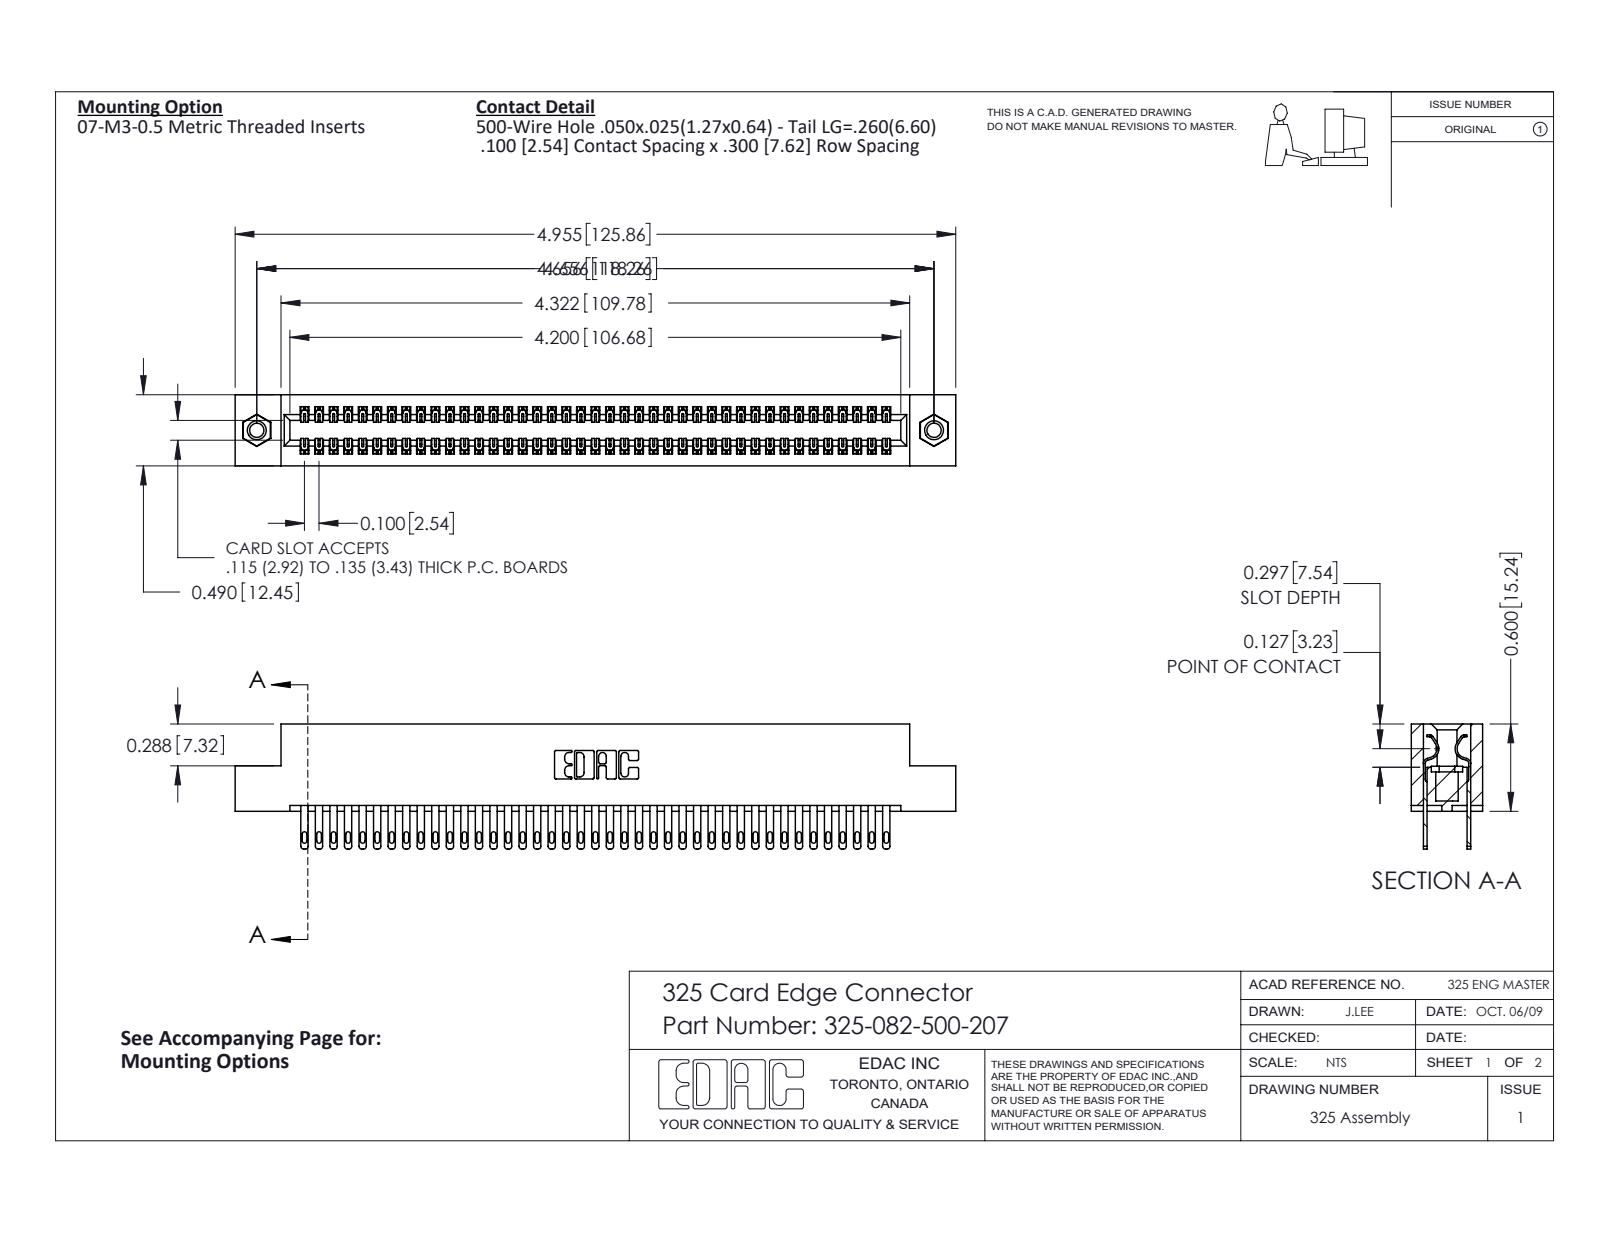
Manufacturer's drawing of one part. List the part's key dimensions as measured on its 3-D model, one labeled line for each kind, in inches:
Part name (STEP PRODUCT): 325 Part_TI; 345-250-001_345-250-005-103; 325-082-500-207; 325-292-001_325-293-100
STEP written by: SolidWorks 2016 (CONFIG_CONTROL_DESIGN)
Units: inches
Bodies: 85 solids, 4110 faces (2562 planar, 1532 cylindrical, 16 other)
Overall size (bounding box): 4.955 × 0.86 × 0.49
Volume: 1.005 in³ · Surface area: 32.24 in²
Round holes (diameter × count): ⌀0.098 ×2, ⌀0.125 ×2, ⌀0.16 ×2
Round bosses / shafts (diameter × count): ⌀0.155 ×2
Partial cylindrical surfaces — rounded edges, fillets, slot ends (radius × count): R0.006 ×123, R0.016 ×82, R0.02 ×82, R0.01 ×22, R0.007 ×6, R0.031 ×6, R0.026 ×3, R0.014 ×2
Main face-to-face distances: 0.083, 0.407, 0.3, 0.107, 0.383, 0.025, 0.49, 0.325, 0.275, 0.56
Hole centre spacings: 4.656
